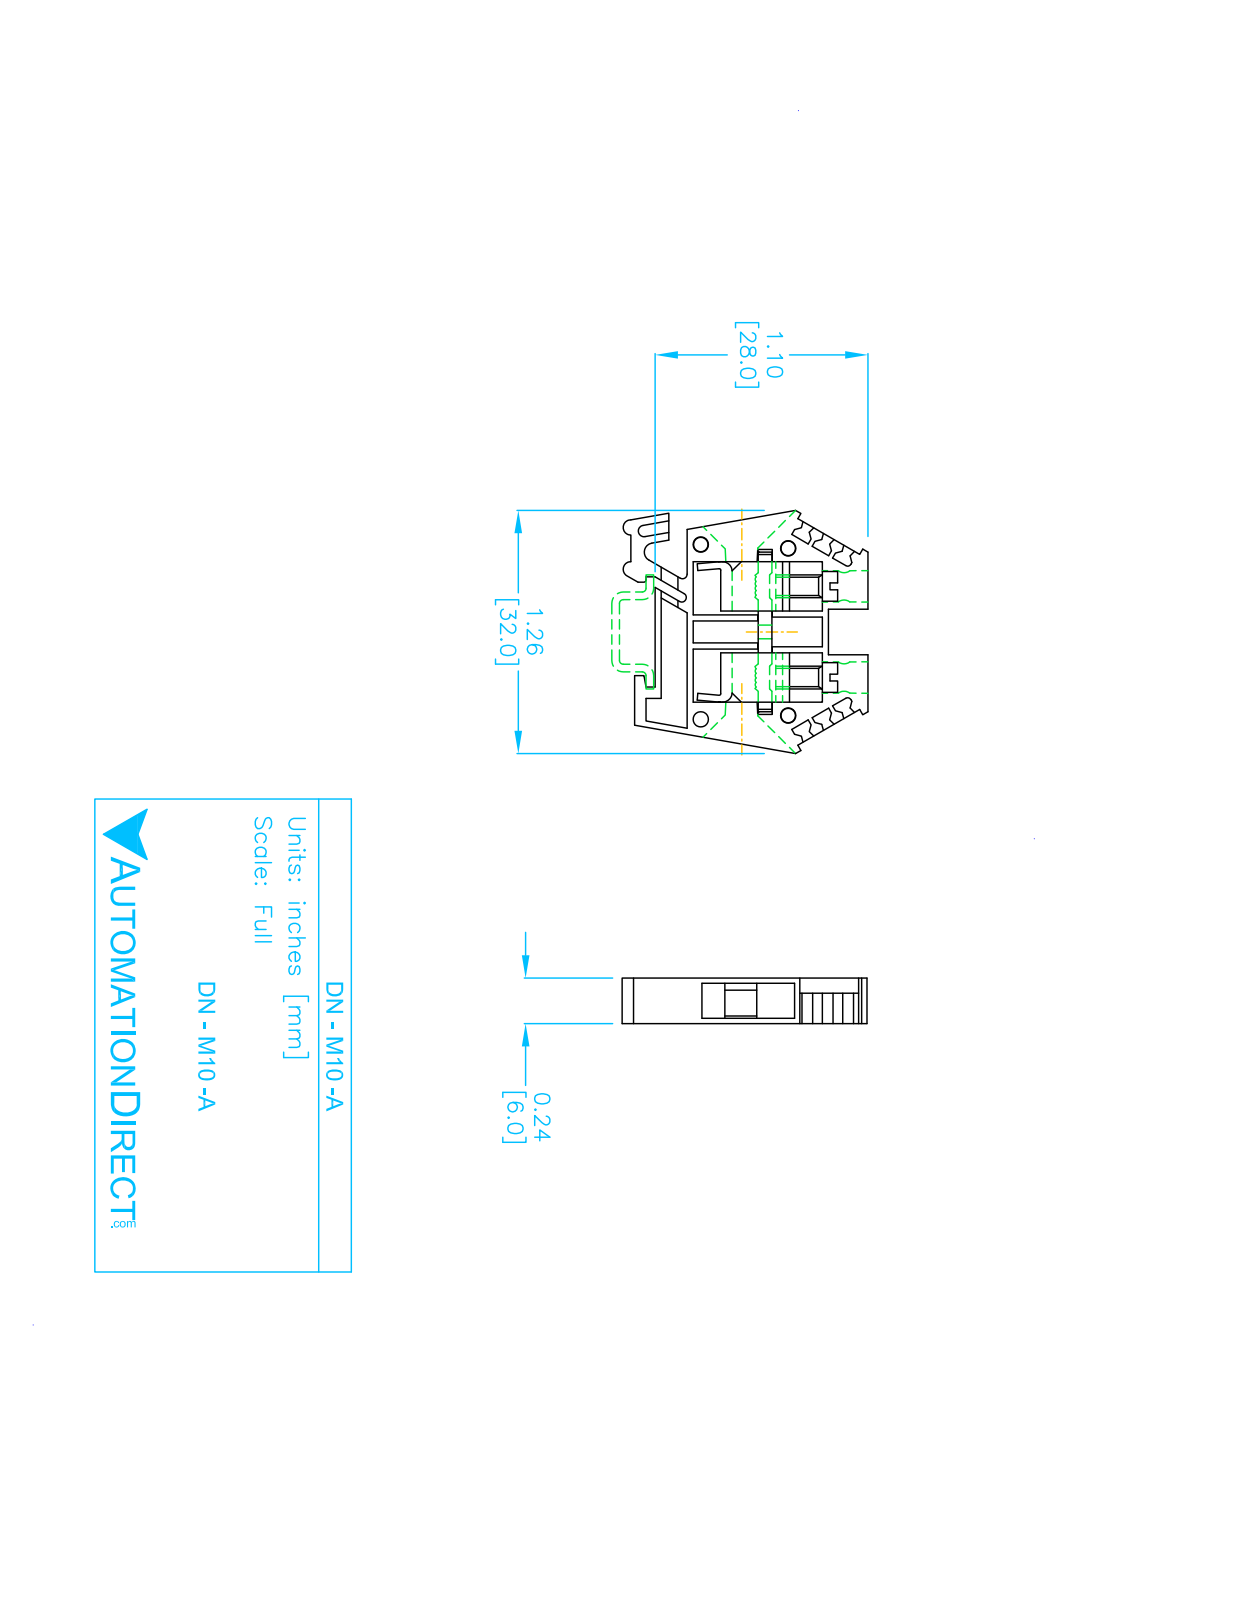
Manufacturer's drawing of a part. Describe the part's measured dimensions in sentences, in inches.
The part is named "43427_DN-M10-A". Its 3-D file was written by "SolidWorks 2013 (AUTOMOTIVE_DESIGN)". It is 1 solid with 174 faces: 137 planar, 29 cylindrical and 8 other. Overall it measures 1.268 by 1.26 by 0.236 inches. Its volume is 0.223 cubic inches and its surface area 4.996 square inches. Round holes: 2 of diameter 0.161. Partial cylindrical surfaces (rounded edges, fillets, slot ends): 6 of radius 0.02, 2 of radius 0.024, 2 of radius 0.039, 1 of radius 0.012, 1 of radius 0.03, 1 of radius 0.047, 1 of radius 0.077. The main face-to-face distances are 0.236, 0.087, 0.059, 0.122, 0.031, 0.15, 0.028, 0.209, 0.165, 0.134. The hole center spacings are 0.472.
